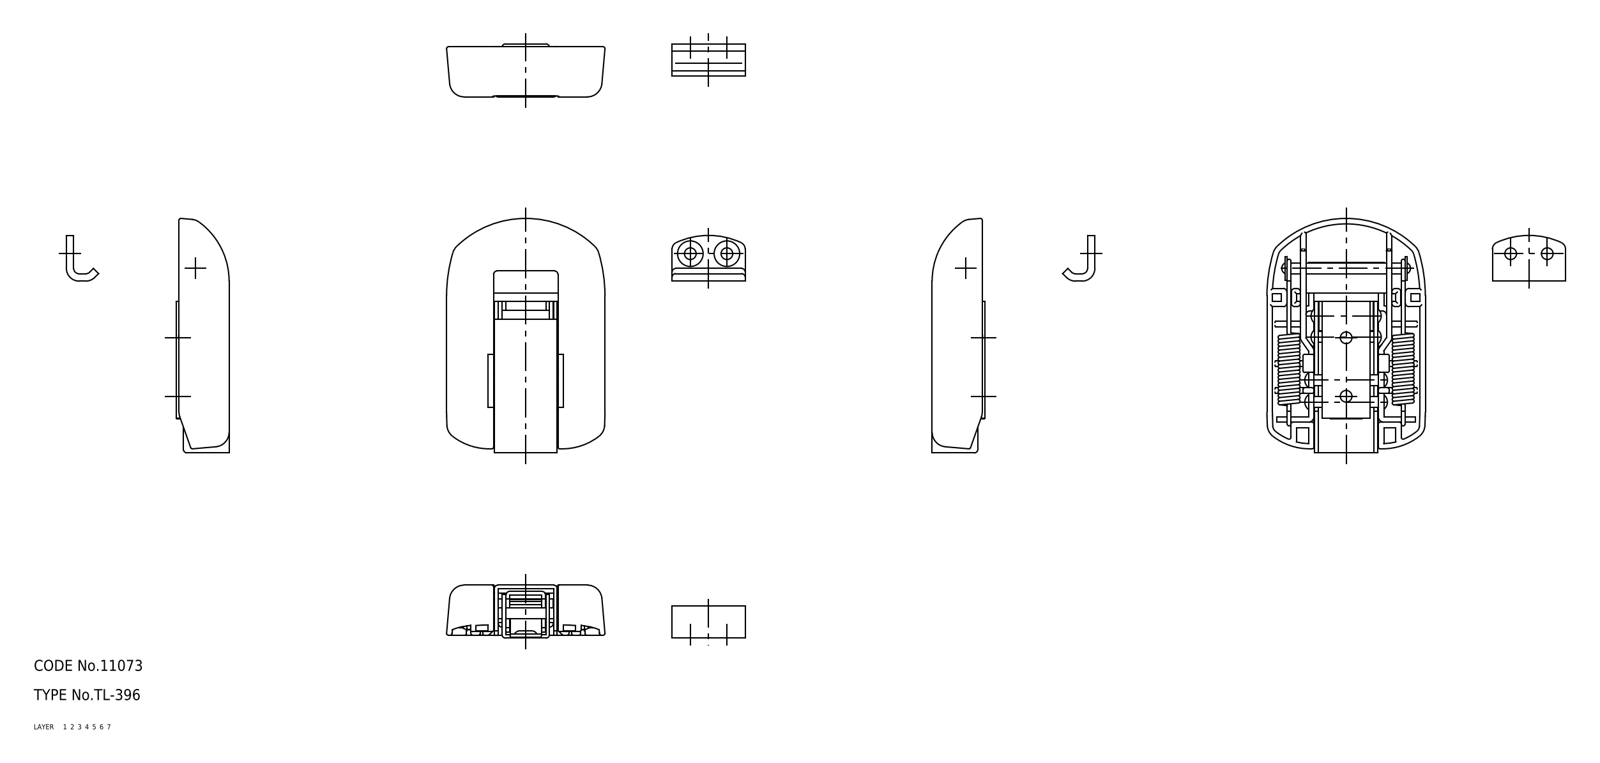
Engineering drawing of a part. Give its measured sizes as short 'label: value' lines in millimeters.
name: shaft; cover; TL_396; base (+3 more)
written by: SolidWorks 2015 (AUTOMOTIVE_DESIGN)
unit: mm
bodies: 8 solids, 564 faces (291 planar, 185 cylindrical, 88 other)
size: 64.2 × 43.4 × 14.5
volume: 12 535 mm³; area: 21 007 mm²
holes: 4× ⌀3.2, 2× ⌀2.6, 2× ⌀3.1
bosses: 6× ⌀1, 5× ⌀3, 1× ⌀6.5, 1× ⌀4.4
rounds: 40× R1, 8× R2, 7× R2.5, 7× R4, 6× R0.5, 6× R1.5, 2× R1.3, 2× R1.55
face distances: 1.5, 1, 2.2, 13, 1.2, 2.1, 1.1, 21.3, 12, 16.4
hole spacings: 23.54, 39.32, 10, 16, 17.6, 31.2
